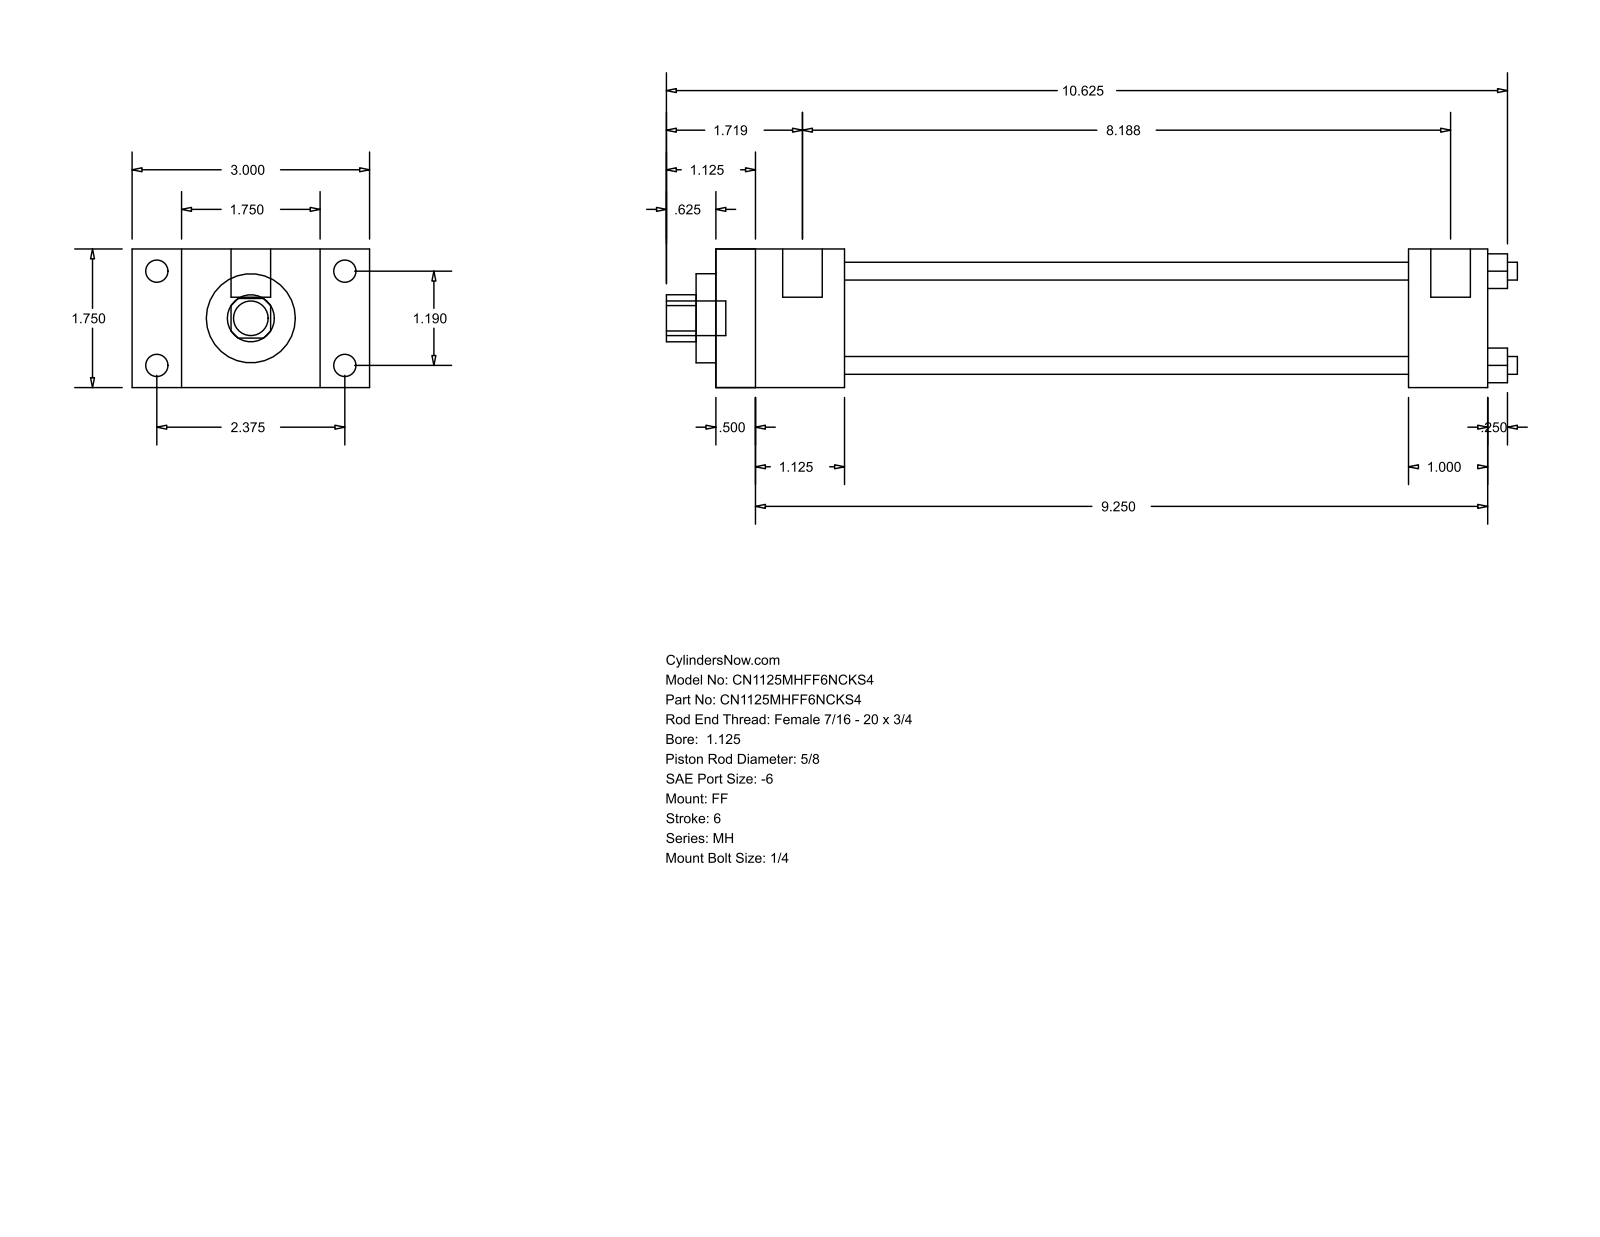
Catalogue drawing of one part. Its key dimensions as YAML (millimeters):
part_name: "MH_FF__0112_0.625"
step_written_by: "GSSL Pune (CONFIG_CONTROL_DESIGN)"
units: millimeters
bodies: {solids: 0, faces: 92, planar: 64, cylindrical: 28, other: 0}
overall_size: [273.05, 76.2, 44.45]
round_holes:
  - {diameter: 5.71, count: 4}
  - {diameter: 15.88, count: 1}
  - {diameter: 28.57, count: 1}
  - {diameter: 34.92, count: 1}
round_bosses_or_shafts:
  - {diameter: 7.14, count: 4}
  - {diameter: 5.56, count: 4}
  - {diameter: 12.7, count: 2}
  - {diameter: 11.11, count: 1}
partial_cylinders:
  - {radius: 7.54, count: 1}
face_to_face_distances: [44.46, 247.64, 15.87, 12.69, 234.95, 60.33, 28.58, 41.27, 222.24, 209.55]
hole_center_spacings: [21.37, 30.22, 42.74]
